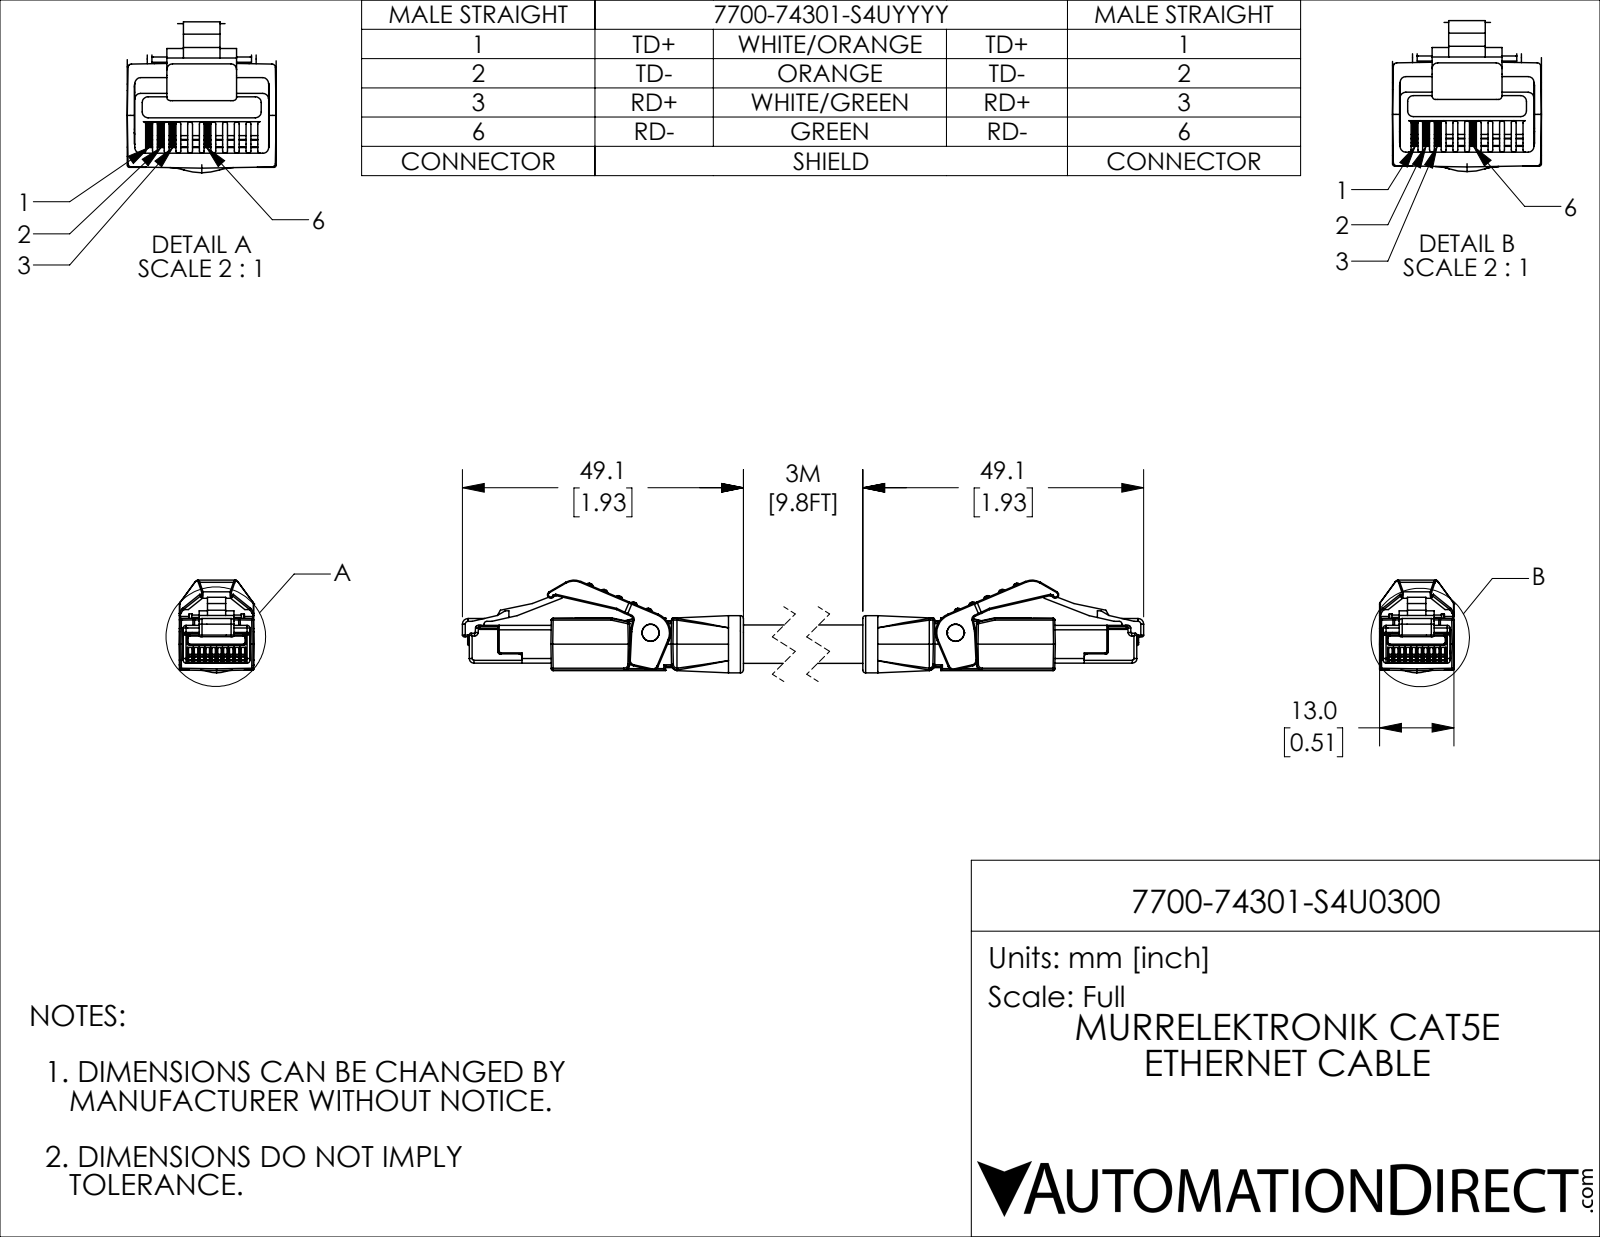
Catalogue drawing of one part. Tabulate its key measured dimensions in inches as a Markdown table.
| quantity | value |
| --- | --- |
| part name | 7700-74301-S4U0300_1; 7700-74301-S4U0300 |
| STEP written by | SolidWorks 2021 (CONFIG_CONTROL_DESIGN) |
| units | inches |
| bodies | 2 solids, 1406 faces (568 planar, 566 cylindrical, 272 other) |
| overall size | 5.112 × 0.638 × 0.512 |
| volume | 0.668 in³ |
| surface area | 10.82 in² |
| round holes (diameter × count) | 0.118 × 2 |
| round bosses / shafts (diameter × count) | 0.117 × 2, 0.394 × 1, 0.264 × 1 |
| partial cylindrical surfaces (radius × count) | 0.008 × 136, 0.012 × 114, 0.004 × 40, 0.02 × 36, 0.039 × 10, 0.031 × 6, 0.079 × 4, 0.197 × 4 |
| main face-to-face distances | 0.512, 0.362, 0.024, 0.488, 0.026, 0.26, 0.069, 0.443, 0.045, 0.419 |
| hole center spacings | 2.526 |
